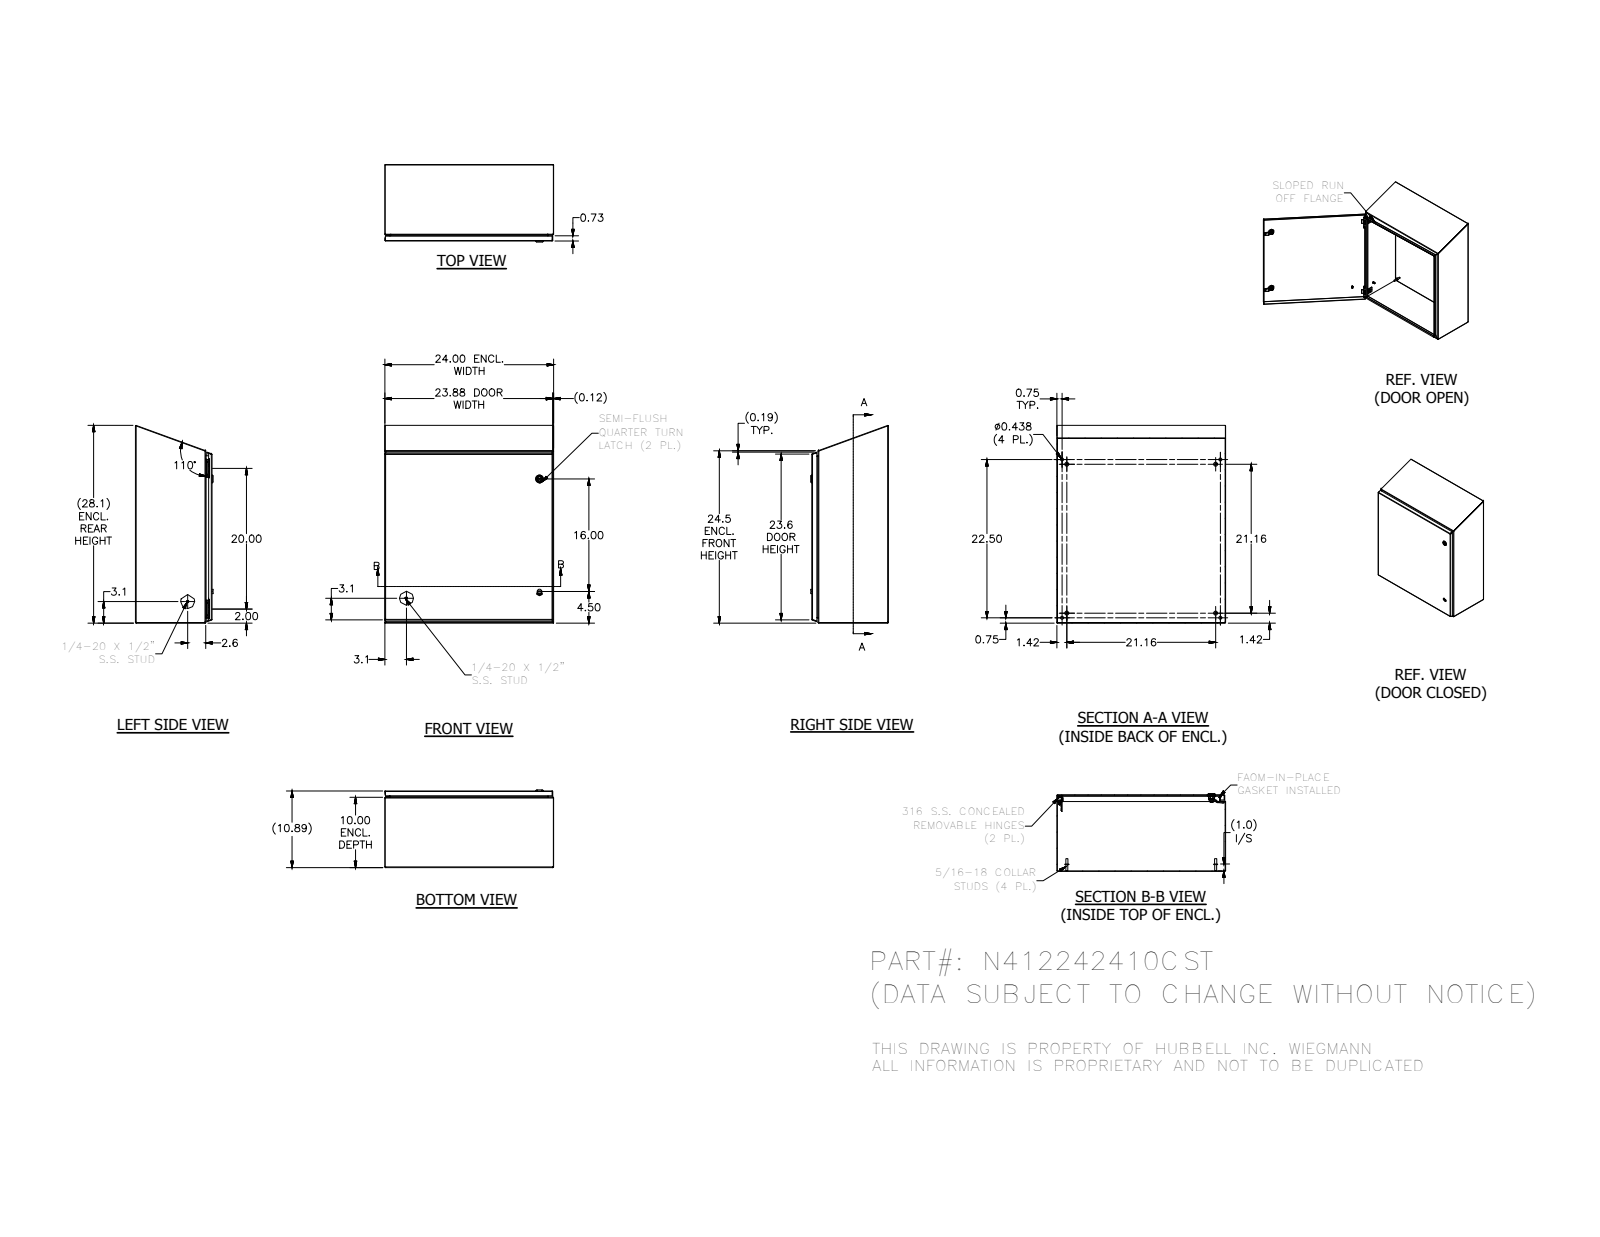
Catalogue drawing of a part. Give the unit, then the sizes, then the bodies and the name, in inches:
Units: inches
Overall size (bounding box): 28.119 × 24 × 11.044
Round holes (diameter × count): ⌀0.093 ×4, ⌀0.152 ×4, ⌀0.167 ×4, ⌀0.172 ×4, ⌀0.187 ×4, ⌀0.437 ×4, ⌀0.156 ×3, ⌀0.197 ×2, ⌀0.315 ×2, ⌀0.394 ×2, ⌀0.402 ×2, ⌀0.634 ×2
Round bosses / shafts (diameter × count): ⌀0.25 ×10, ⌀0.563 ×4, ⌀0.36 ×4, ⌀0.32 ×4, ⌀0.3 ×4, ⌀0.275 ×4, ⌀0.256 ×4, ⌀0.164 ×4
Partial cylindrical surfaces — rounded edges, fillets, slot ends (radius × count): R0.012 ×54, R0.031 ×29, R0.05 ×26, R0.02 ×23, R0.105 ×19, R0.016 ×18, R0.125 ×16, R0.032 ×8
Main face-to-face distances: 0.074, 10.813, 10.887, 10.739, 23.926, 23.852, 24, 9.926, 0.887, 0.813
Hole centre spacings: 20, 22.5, 22.869, 0.5, 0.656, 0.66, 1.307, 1.311
Volume: 184 in³ · Surface area: 4 990 in²
Bodies: 44 solids, 1921 faces (767 planar, 690 cylindrical, 464 other)
Part name (STEP PRODUCT): N412242410CST
STEP written by: SolidWorks 2018 (AUTOMOTIVE_DESIGN)
